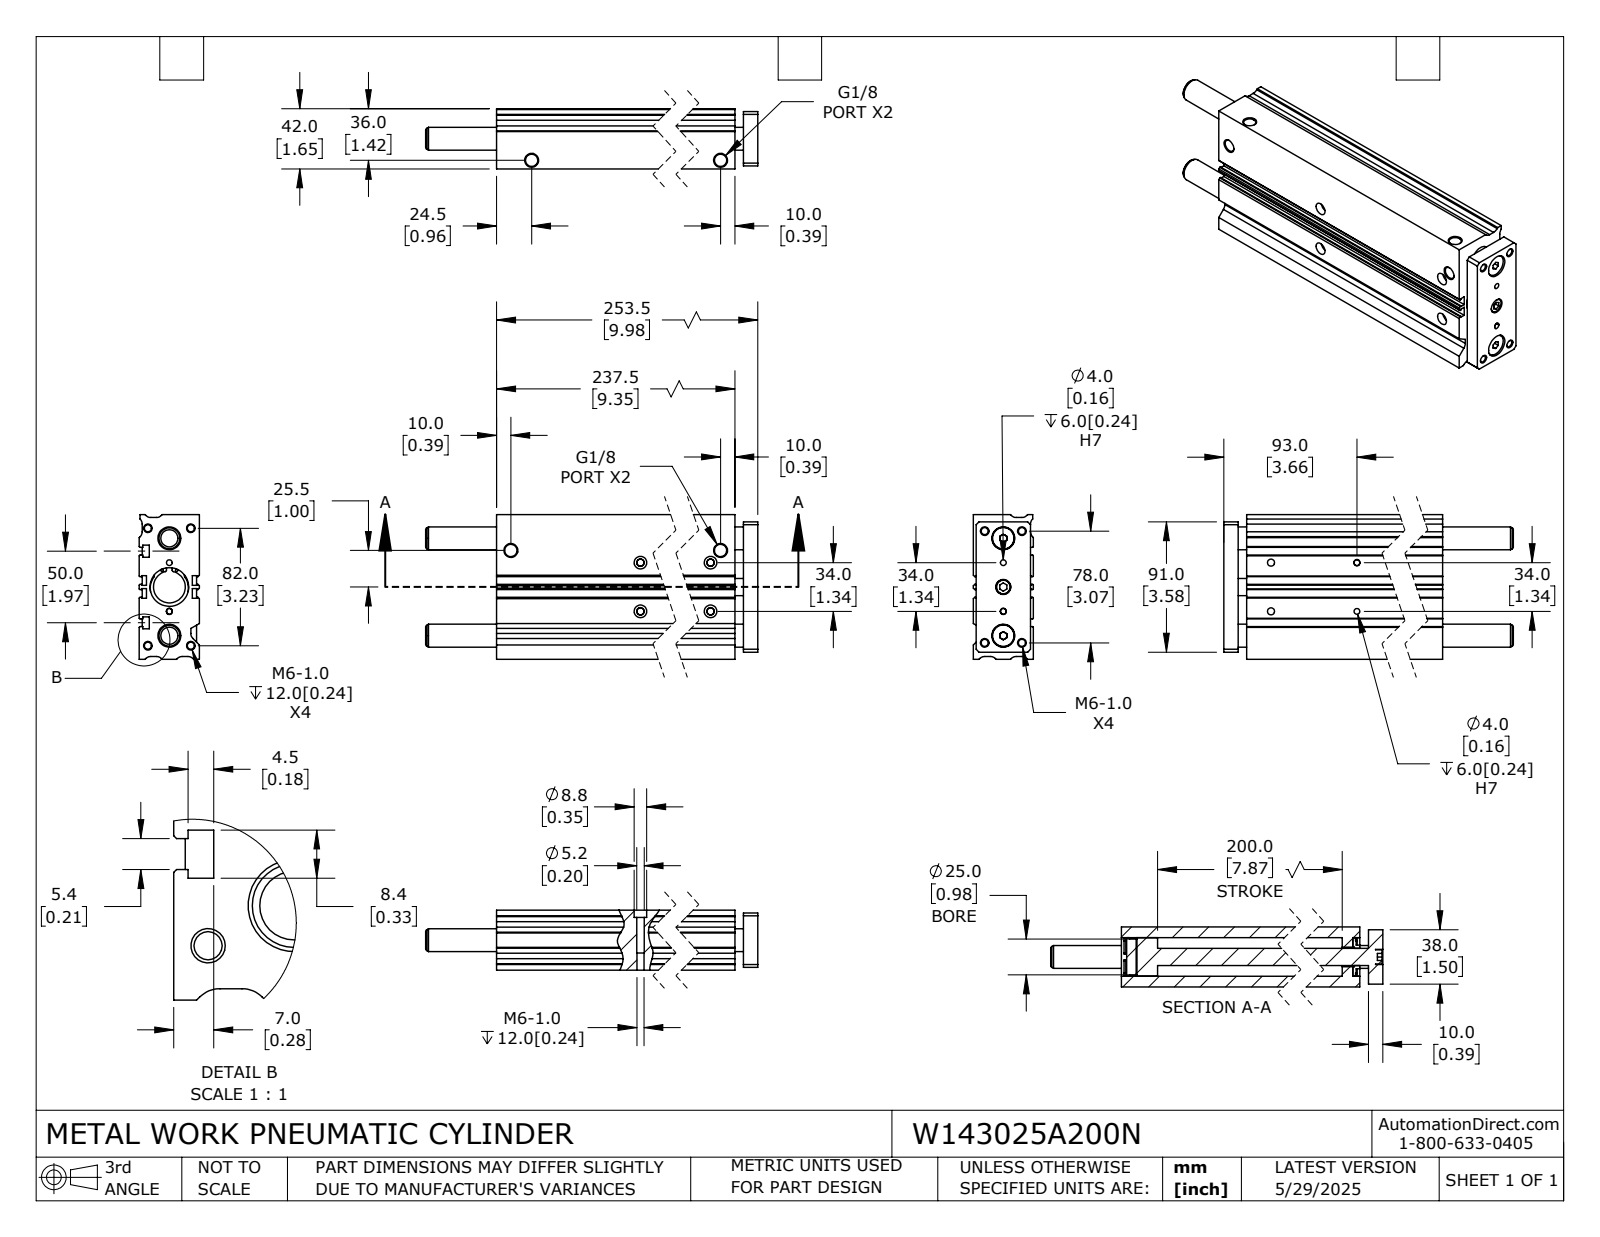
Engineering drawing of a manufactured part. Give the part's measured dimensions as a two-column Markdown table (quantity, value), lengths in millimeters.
| quantity | value |
| --- | --- |
| part name | W143025A200N_ROD; W143025A200N; W143025A200N_BODY |
| STEP written by | SolidWorks 2024 (CONFIG_CONTROL_DESIGN) |
| units | millimeters |
| bodies | 6 solids, 390 faces (191 planar, 157 cylindrical, 42 other) |
| overall size | 303 × 101 × 42 |
| volume | 872 400 mm³ |
| surface area | 201 400 mm² |
| round holes (diameter × count) | 4.9 × 8, 1.7 × 4, 4 × 4, 4.9 × 4, 5.2 × 4, 8.6 × 4, 8.8 × 4, 16 × 2, 10.5 × 1, 12 × 1, 13.7 × 1, 22.2 × 1 |
| round bosses / shafts (diameter × count) | 15.5 × 2, 27 × 1, 25 × 1, 16.5 × 1, 10 × 1 |
| partial cylindrical surfaces (radius × count) | 1 × 12, 5 × 9, 2 × 8, 13.3 × 2, 14.2 × 1 |
| main face-to-face distances | 42, 2, 5, 35, 37, 21.3, 101, 58.4, 7, 9 |
| hole center spacings | 34, 2.8, 7.4, 12.7, 13.9, 16.6, 17, 22.9 |
